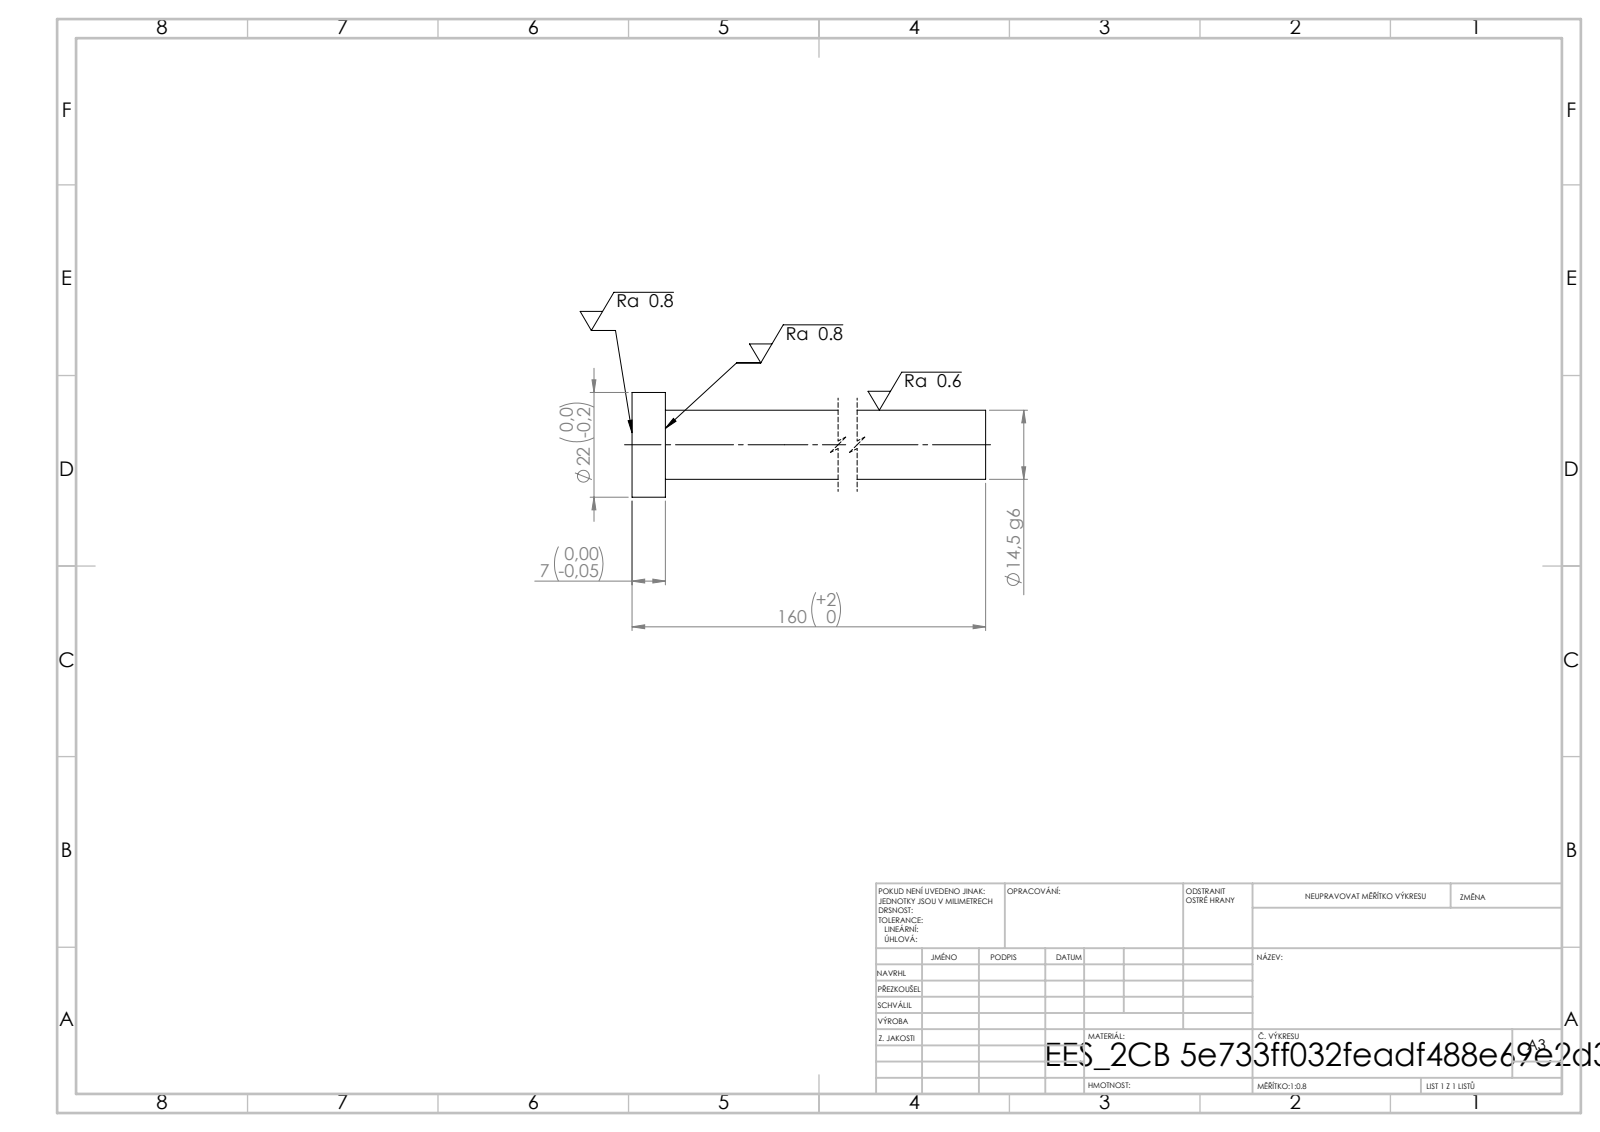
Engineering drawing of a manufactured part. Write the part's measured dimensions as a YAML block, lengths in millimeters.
step_written_by: "SolidWorks 2019 (CONFIG_CONTROL_DESIGN)"
units: millimeters
bodies: {solids: 1, faces: 7, planar: 3, cylindrical: 4, other: 0}
overall_size: [160, 22, 22]
volume: 27926
surface_area: 8214
round_bosses_or_shafts:
  - {diameter: 22, count: 1}
  - {diameter: 14.5, count: 1}
face_to_face_distances: [7, 160, 153]
